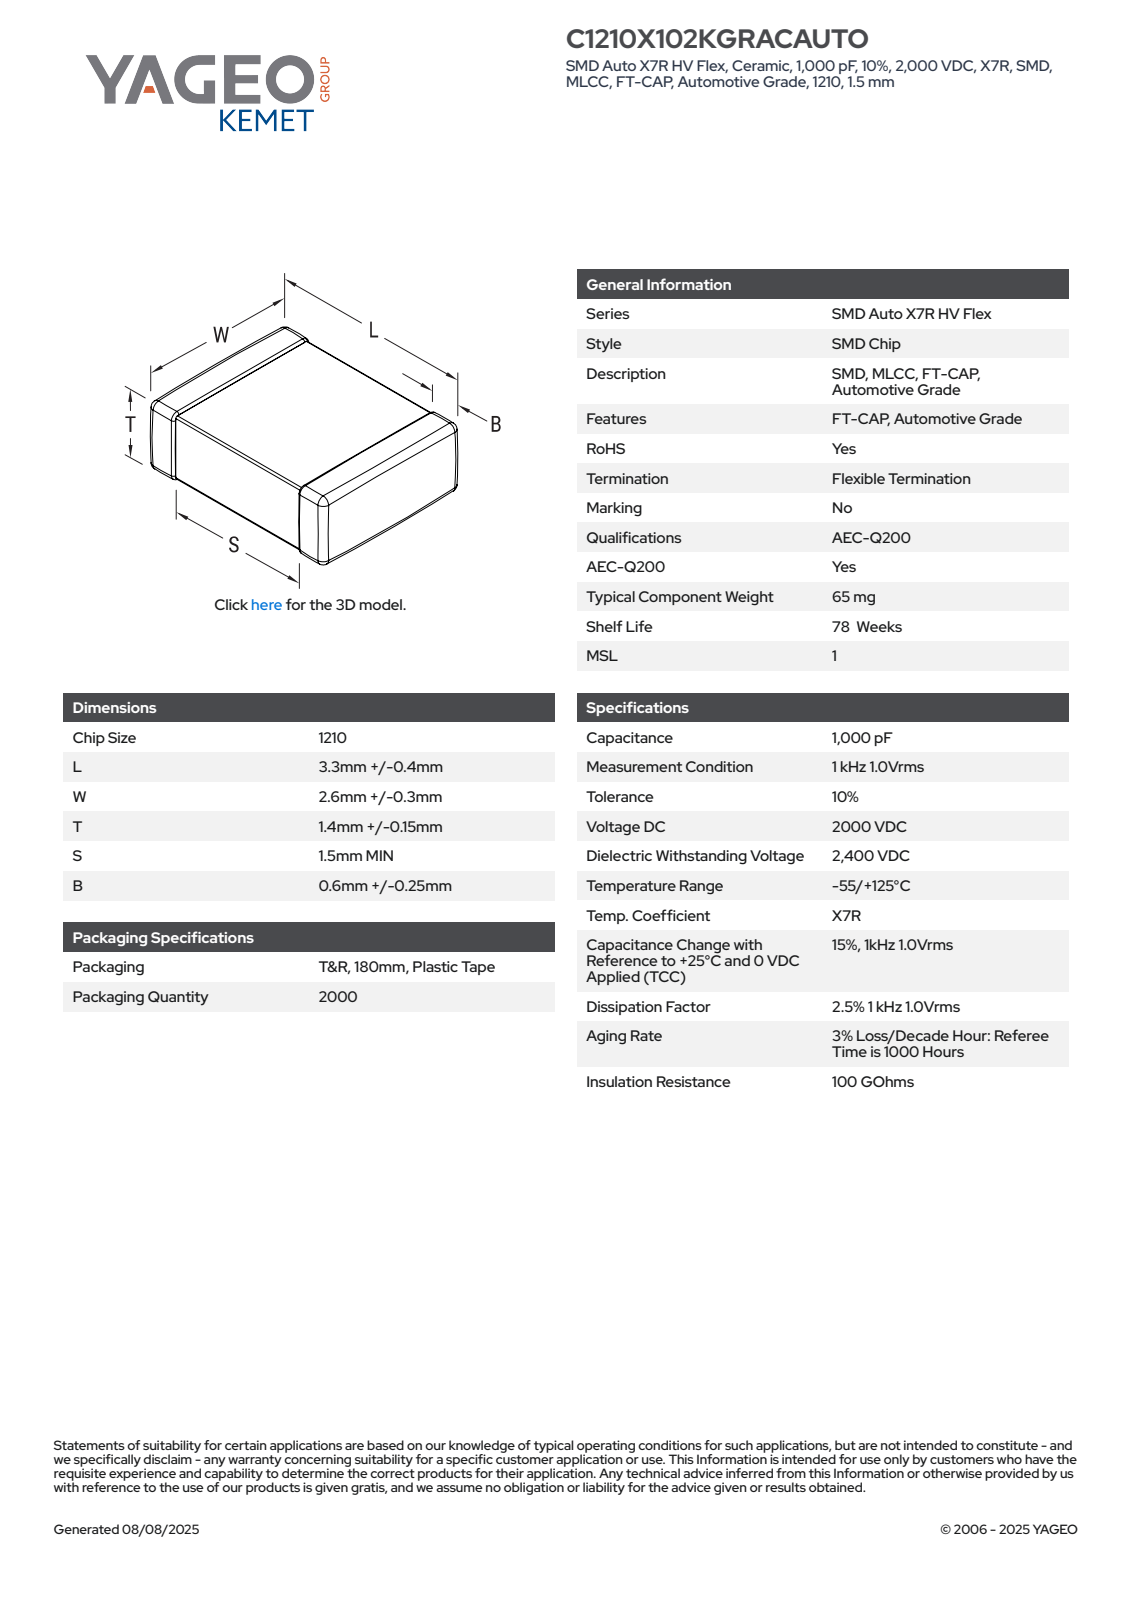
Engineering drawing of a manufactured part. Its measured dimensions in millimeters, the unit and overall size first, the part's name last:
Units: millimetres
Overall size (bounding box): 3.7 × 2.9 × 1.55
Main face-to-face distances: 1.49, 1.43, 2.84, 1.55, 3.7, 2.78, 2.9, 0.43, 1.57, 2.13
Volume: 16 mm³ · Surface area: 42 mm²
Bodies: 4 solids, 125 faces (71 planar, 38 cylindrical, 16 other)
Part name (STEP PRODUCT): CCS_CCSTD_1210_L3.7W2.9T1.55B0.6
STEP written by: SolidWorks 2021 (AUTOMOTIVE_DESIGN)
